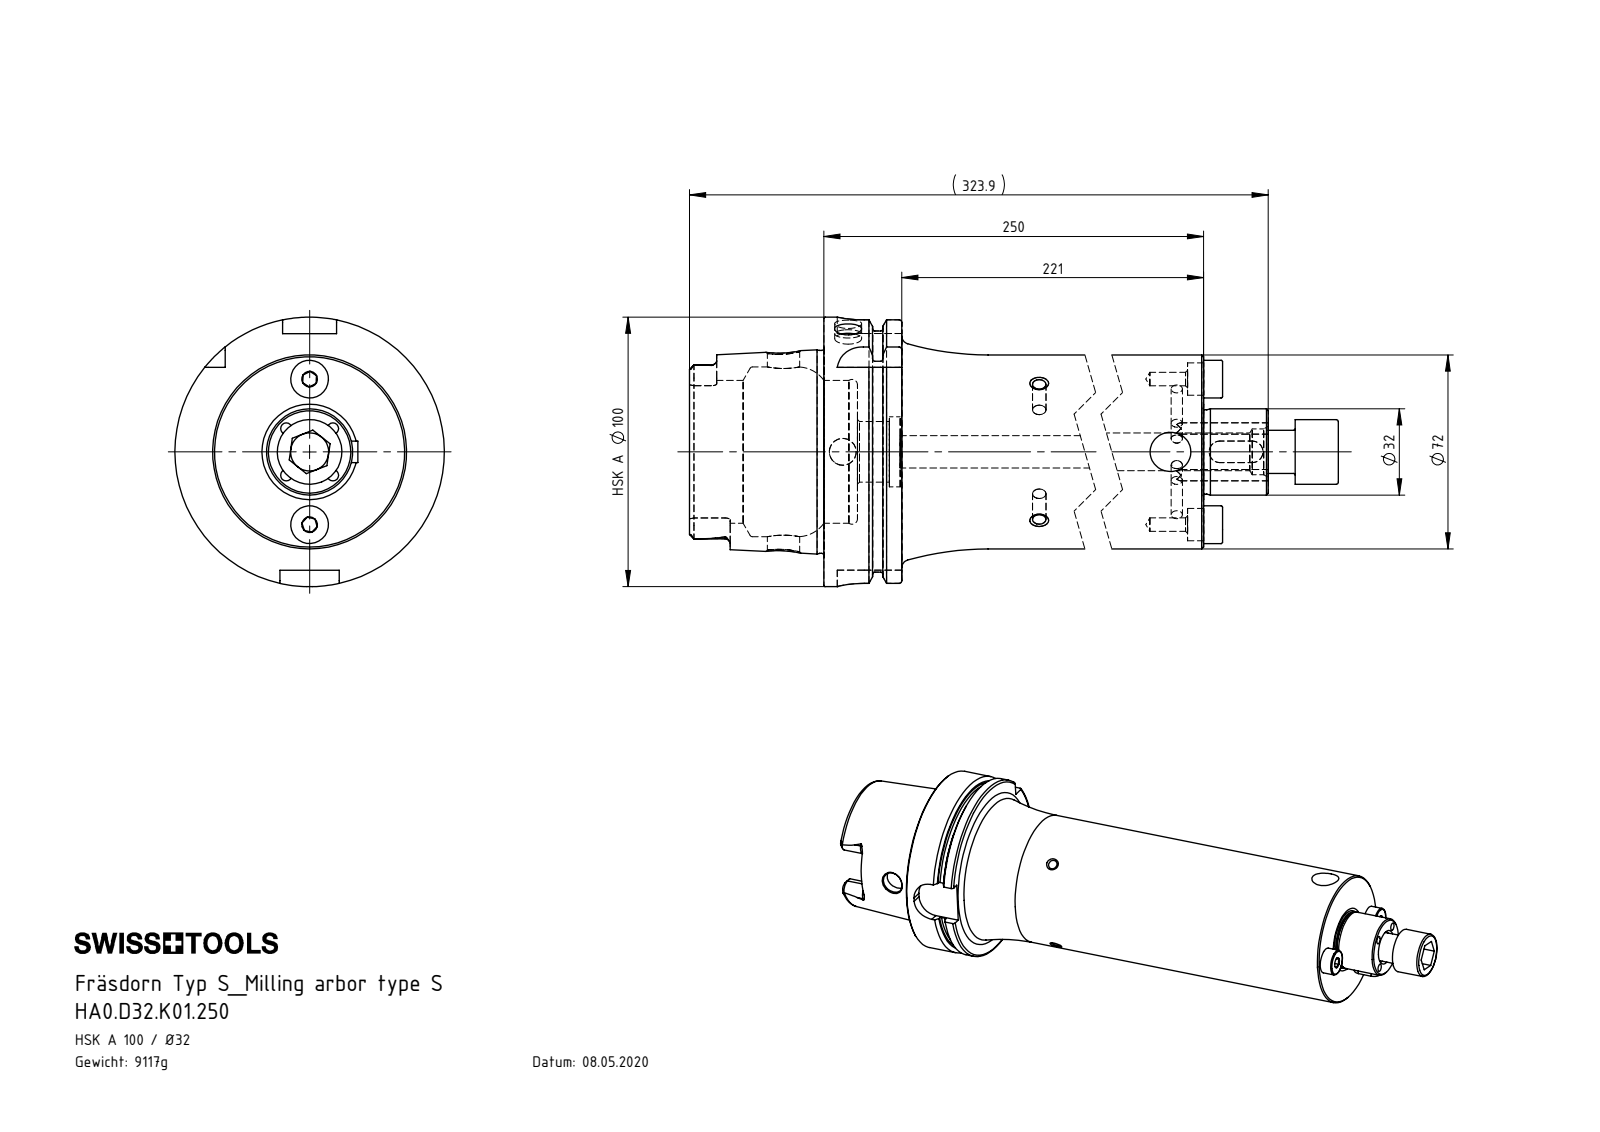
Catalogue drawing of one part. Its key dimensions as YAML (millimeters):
part_name: "D32-ER2.001.022_C; HA0-D32.K01.250_B_Fertigbearbeitung; D32-ER1.002.035_A; HA0.D32.K01.250 (+1 more)"
step_written_by: "SolidWorks 2017 (AUTOMOTIVE_DESIGN)"
units: millimeters
bodies: {solids: 4, faces: 116, planar: 39, cylindrical: 25, other: 52}
overall_size: [239.05, 72, 72]
volume: 17031
surface_area: 49090
round_bosses_or_shafts:
  - {diameter: 14, count: 2}
  - {diameter: 12, count: 2}
  - {diameter: 6, count: 2}
  - {diameter: 4.6, count: 2}
  - {diameter: 72, count: 1}
  - {diameter: 24, count: 1}
  - {diameter: 16, count: 1}
partial_cylinders:
  - {radius: 4, count: 2}
face_to_face_distances: [8, 43, 16, 27, 14.14, 7, 35, 51, 4, 12]
